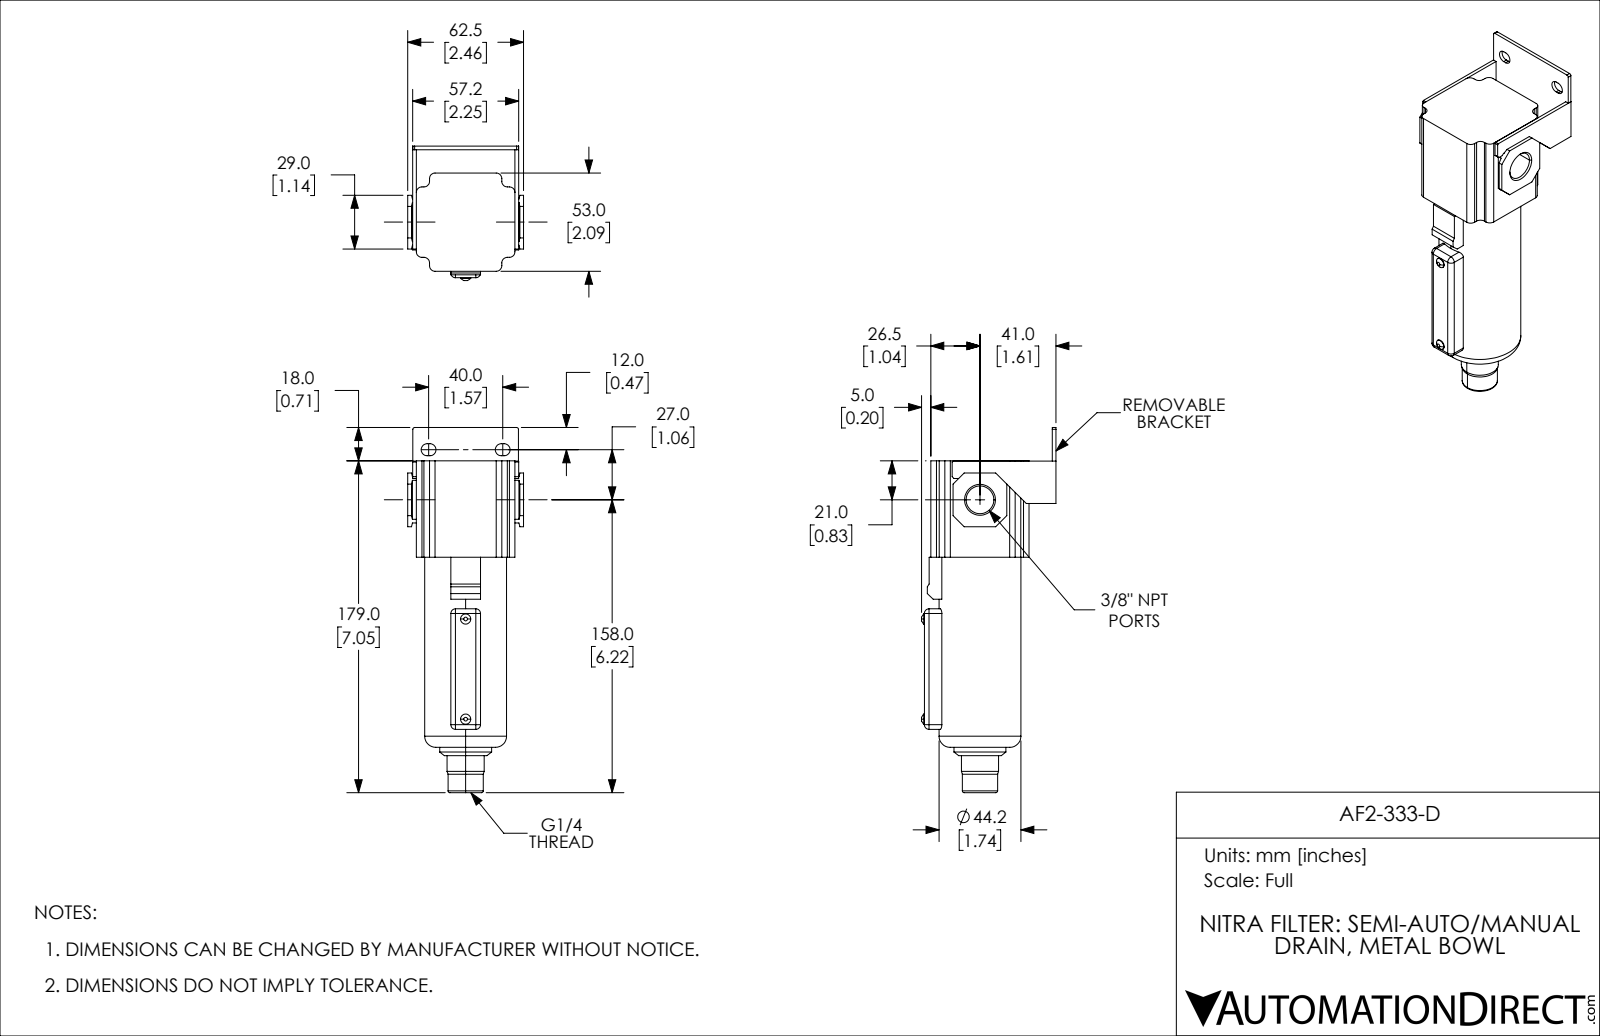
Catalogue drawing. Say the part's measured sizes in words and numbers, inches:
The part is named "AF2-333-D". Its 3-D file was written by "SolidWorks 2019 (CONFIG_CONTROL_DESIGN)". It is 1 solid with 161 faces: 95 planar, 44 cylindrical and 22 other. Overall it measures 7.756 by 2.854 by 2.461 inches. Its volume is 19.42 cubic inches and its surface area 66.1 square inches. Round holes: 1 of diameter 0.337, 1 of diameter 0.589. Round bosses or shafts: 2 of diameter 0.217, 1 of diameter 1.74, 1 of diameter 1.102, 1 of diameter 0.787, 1 of diameter 0.748. Partial cylindrical surfaces (rounded edges, fillets, slot ends): 12 of radius 0.118, 8 of radius 0.098, 4 of radius 0.128, 2 of radius 0.039. The main face-to-face distances are 0.079, 0.492, 0.571, 2.657, 2.579, 2.087, 2.173, 2.094, 0.811, 1.441.
